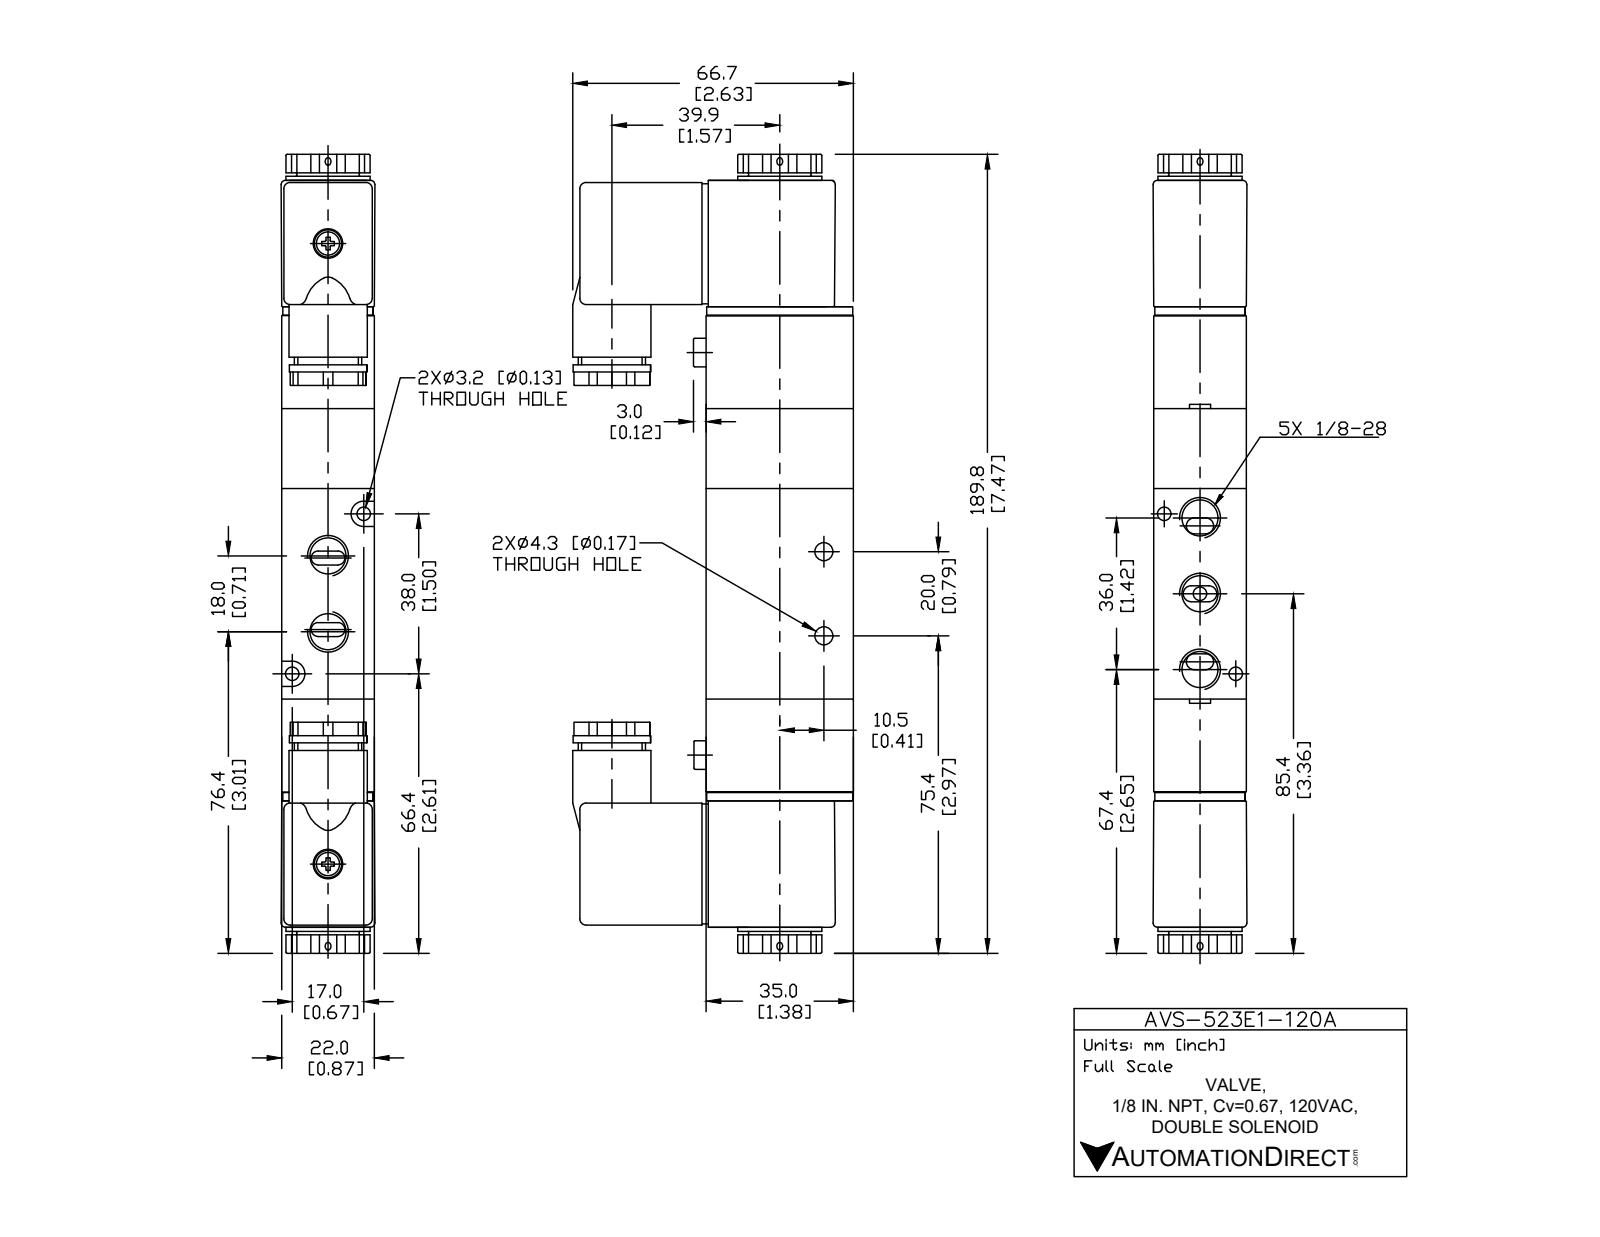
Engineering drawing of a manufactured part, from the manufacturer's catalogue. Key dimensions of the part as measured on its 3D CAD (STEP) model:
Part name (STEP PRODUCT): AVS-523E1-120A
STEP written by: SolidWorks 2015 (CONFIG_CONTROL_DESIGN)
Units: millimetres
Bodies: 5 solids, 236 faces (129 planar, 91 cylindrical, 16 other)
Overall size (bounding box): 189.82 × 66.7 × 22
Volume: 150 497 mm³ · Surface area: 37 557 mm²
Round holes (diameter × count): ⌀8.43 ×5, ⌀3.2 ×2, ⌀4.3 ×2, ⌀9.3 ×1
Round bosses / shafts (diameter × count): ⌀6.8 ×2, ⌀18.6 ×1, ⌀17.6 ×1, ⌀15.81 ×1, ⌀13.02 ×1, ⌀11 ×1
Partial cylindrical surfaces — rounded edges, fillets, slot ends (radius × count): R1.54 ×10, R0.3 ×8, R0.5 ×8, R1 ×8, R3 ×2
Main face-to-face distances: 0.88, 21.74, 1.95, 20.05, 22, 18.1, 22.62, 69, 30.59, 5.03
Hole centre spacings: 8.56, 18, 20.81, 37.96, 7.54, 7.83, 10.53, 10.55
